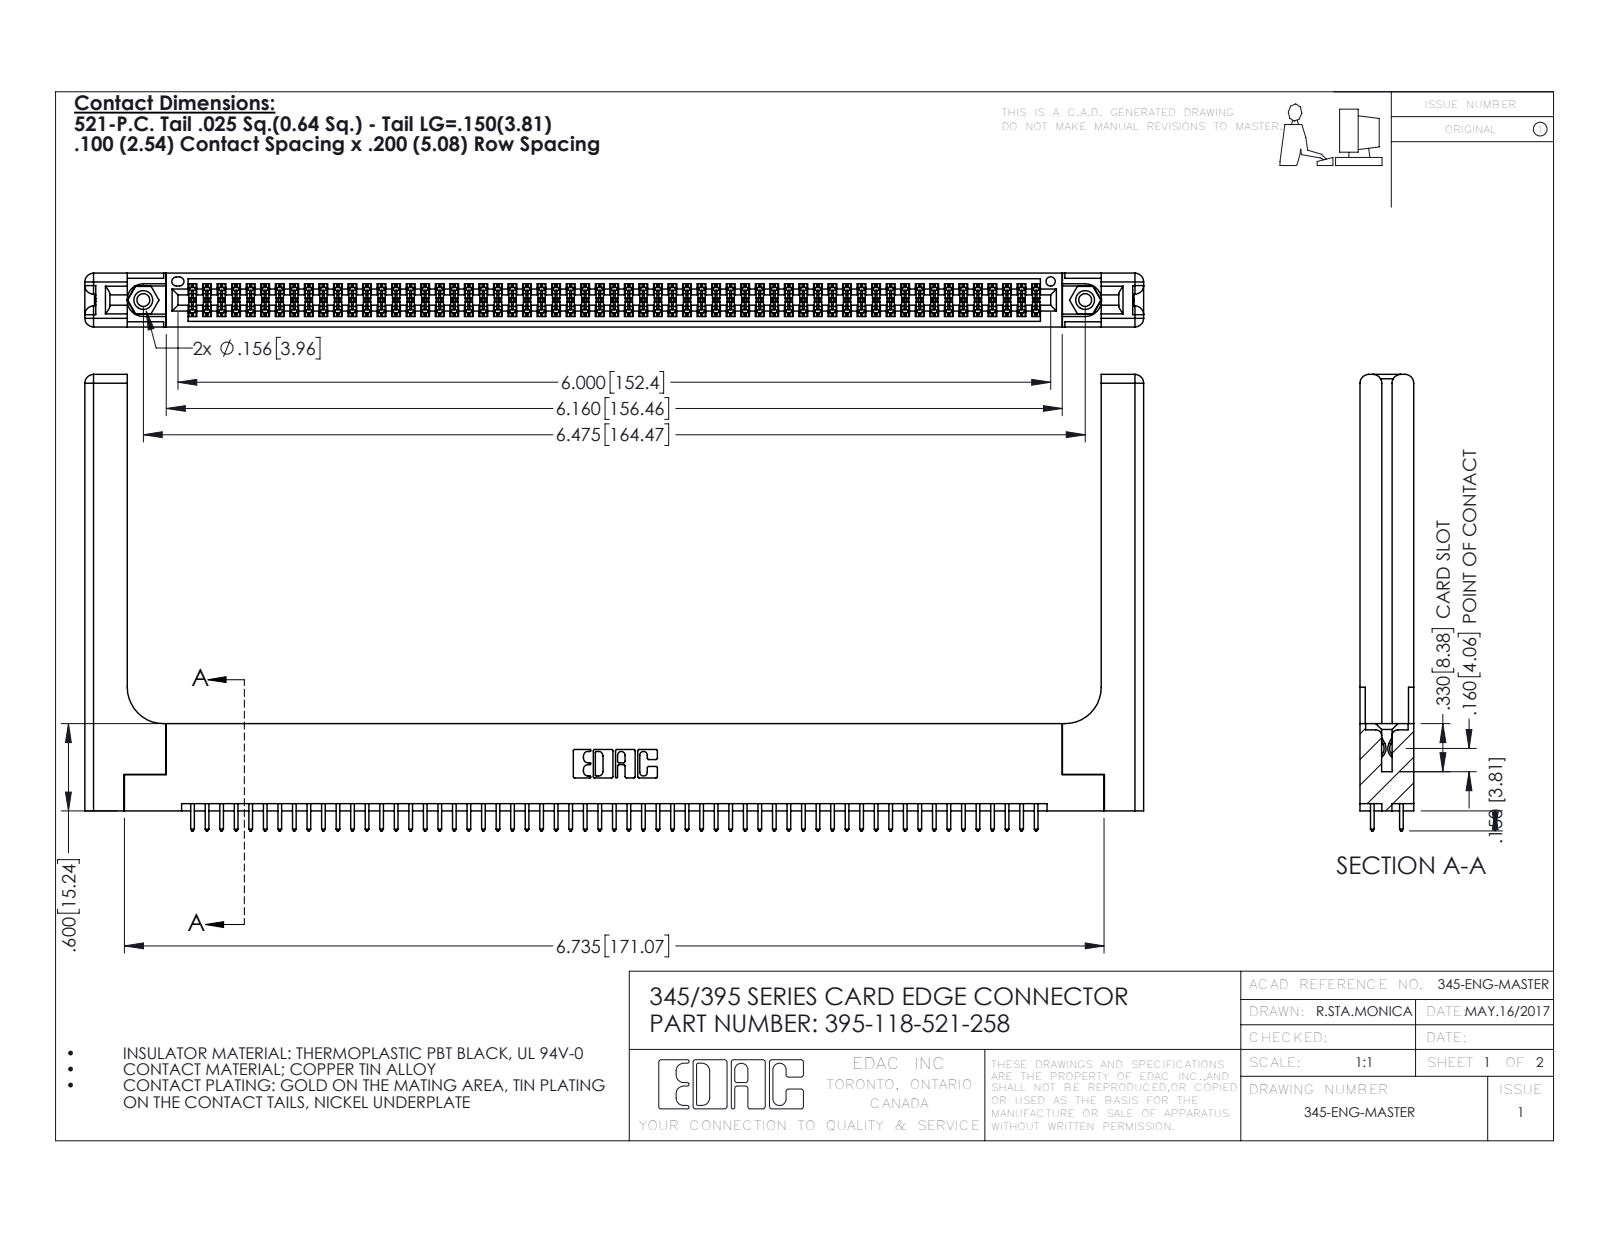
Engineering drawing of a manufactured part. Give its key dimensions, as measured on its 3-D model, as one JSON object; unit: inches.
{"part_name": "345-250-001_345-250-001-102; 345 Part_Flush Mounting Lugs - 0.156 Dia-TH; 345-292-001_345-293-121; 345-220-058_345-220-058 (+1 more)", "step_written_by": "SolidWorks 2016 (CONFIG_CONTROL_DESIGN)", "units": "inches", "bodies": {"solids": 123, "faces": 6282, "planar": 4122, "cylindrical": 2100, "other": 60}, "overall_size": [7.279, 3.137, 0.37], "volume_in3": 1.62, "surface_area_in2": 49.27, "round_holes": [[0.089, 2], [0.125, 2], [0.156, 2], [0.064, 1]], "round_bosses_or_shafts": [[0.155, 2]], "partial_cylinders_radius": [[0.006, 177], [0.01, 118], [0.01, 22], [0.06, 16], [0.007, 6], [0.031, 6], [0.026, 3], [0.014, 2]], "face_to_face_distances": [0.072, 0.298, 0.37, 0.2, 0.098, 0.272, 0.025, 0.225, 0.175, 0.148], "hole_center_spacings": [0.27, 6.239, 6.475]}
